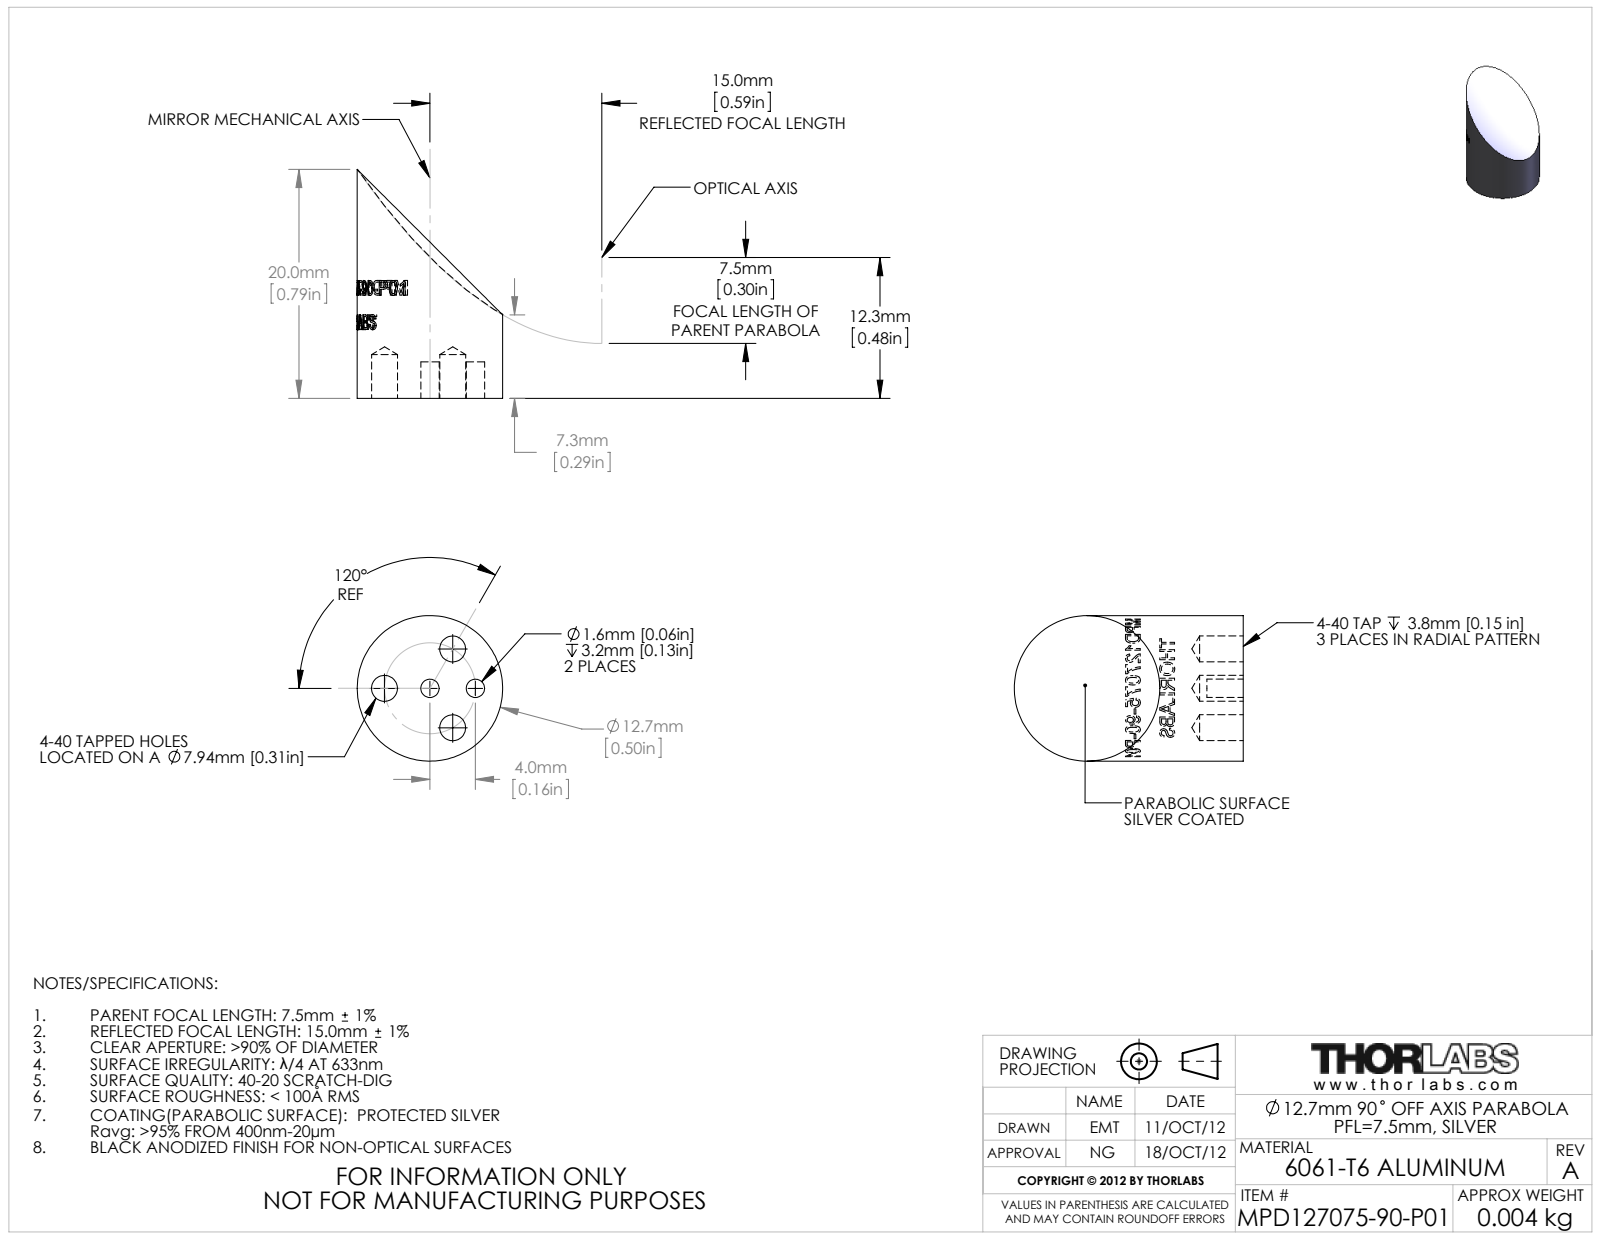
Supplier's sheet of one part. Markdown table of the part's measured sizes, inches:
| quantity | value |
| --- | --- |
| part name | TTN005544-E0W |
| STEP written by | SolidWorks 2012 (CONFIG_CONTROL_DESIGN) |
| units | inches |
| bodies | 1 solid, 60 faces (3 planar, 49 cylindrical, 8 other) |
| overall size | 0.787 × 0.5 × 0.5 |
| volume | 0.096 in³ |
| surface area | 1.5 in² |
| round holes (diameter × count) | 0.089 × 3, 0.063 × 2 |
| round bosses / shafts (diameter × count) | 0.5 × 1 |
| main face-to-face distances | 0.125 |
| hole center spacings | 0.156, 0.27, 0.271, 0.313 |
